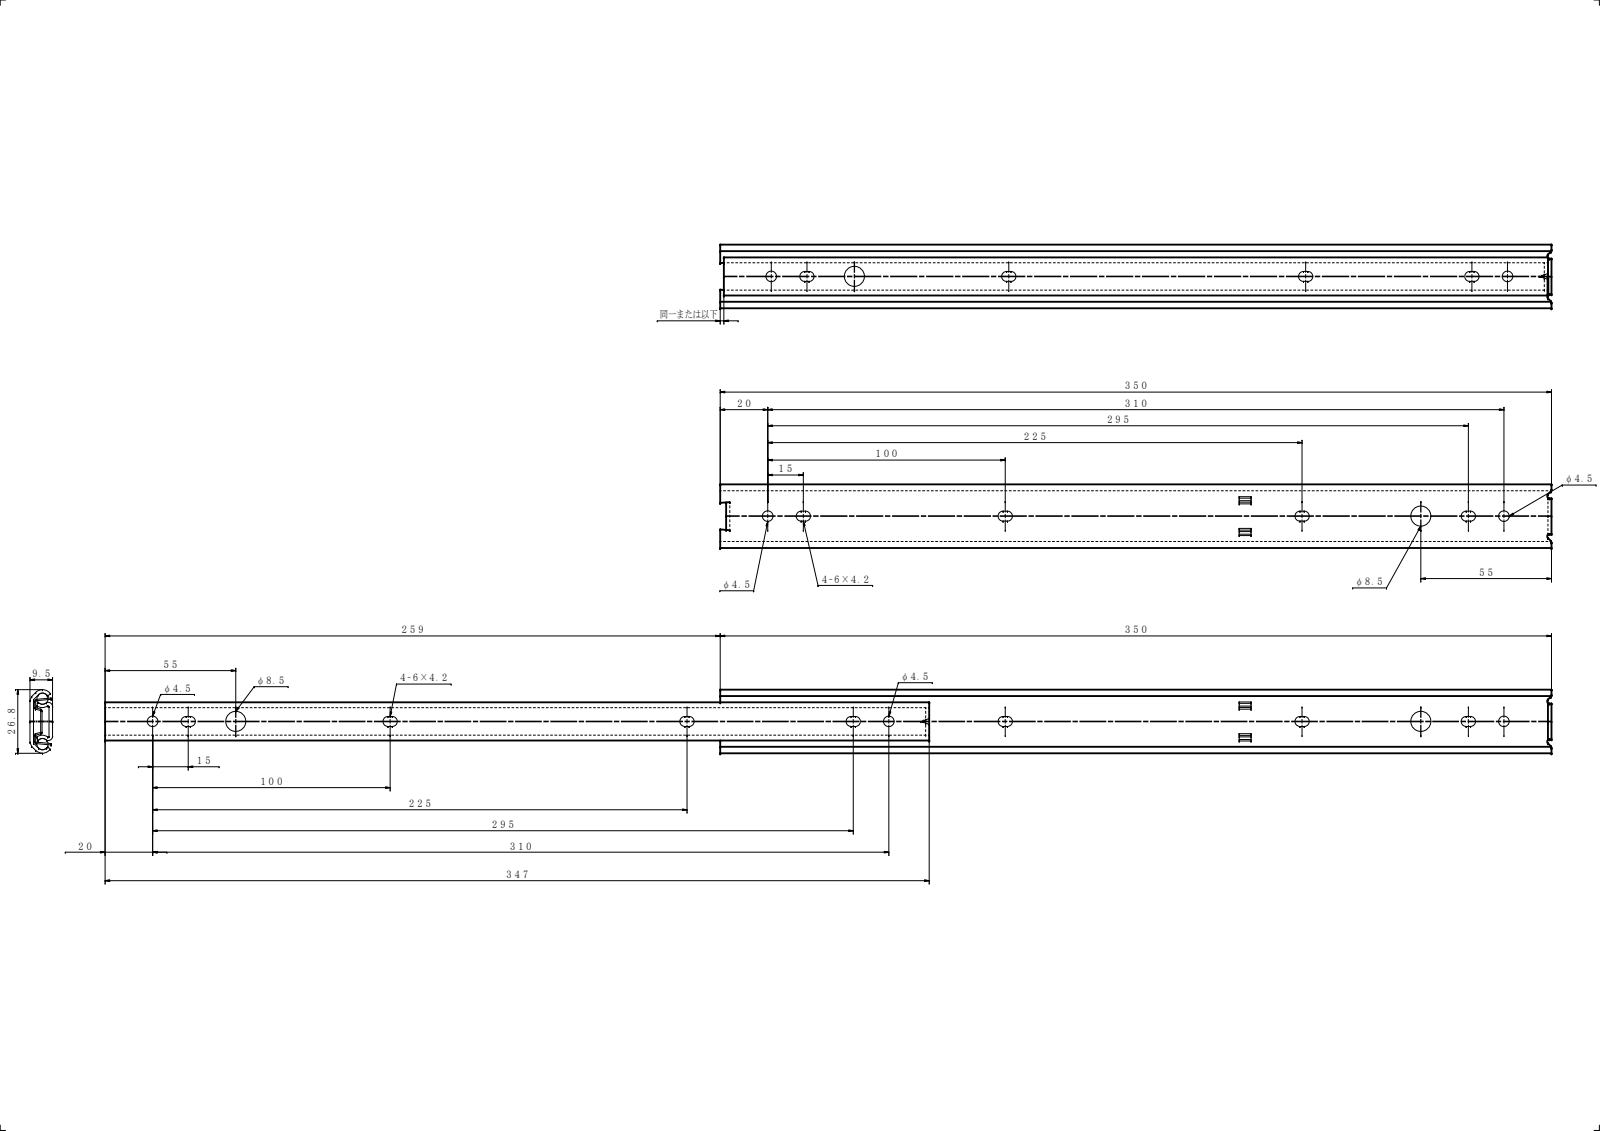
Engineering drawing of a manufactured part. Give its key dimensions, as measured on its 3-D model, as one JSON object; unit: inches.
{"part_name": "U2721_350; U2721-350 IM; U2721-350 OM", "step_written_by": "SolidWorks 2019 (CONFIG_CONTROL_DESIGN)", "units": "inches", "bodies": {"solids": 2, "faces": 134, "planar": 61, "cylindrical": 73, "other": 0}, "overall_size": [23.969, 1.055, 0.374], "volume_in3": 1.96, "surface_area_in2": 70.89, "round_holes": [[0.177, 4], [0.335, 2]], "partial_cylinders_radius": [[0.083, 16], [0.079, 10], [0.039, 5], [0.02, 4], [0.007, 2], [0.051, 2], [0.066, 2], [0.094, 2]], "face_to_face_distances": [0.059, 0.315, 0.374, 0.256, 10.307, 10.248, 13.623, 3.316, 10.366, 13.682], "hole_center_spacings": [1.378, 8.811, 10.189, 10.827, 12.205, 21.016, 2.016, 19.638]}
